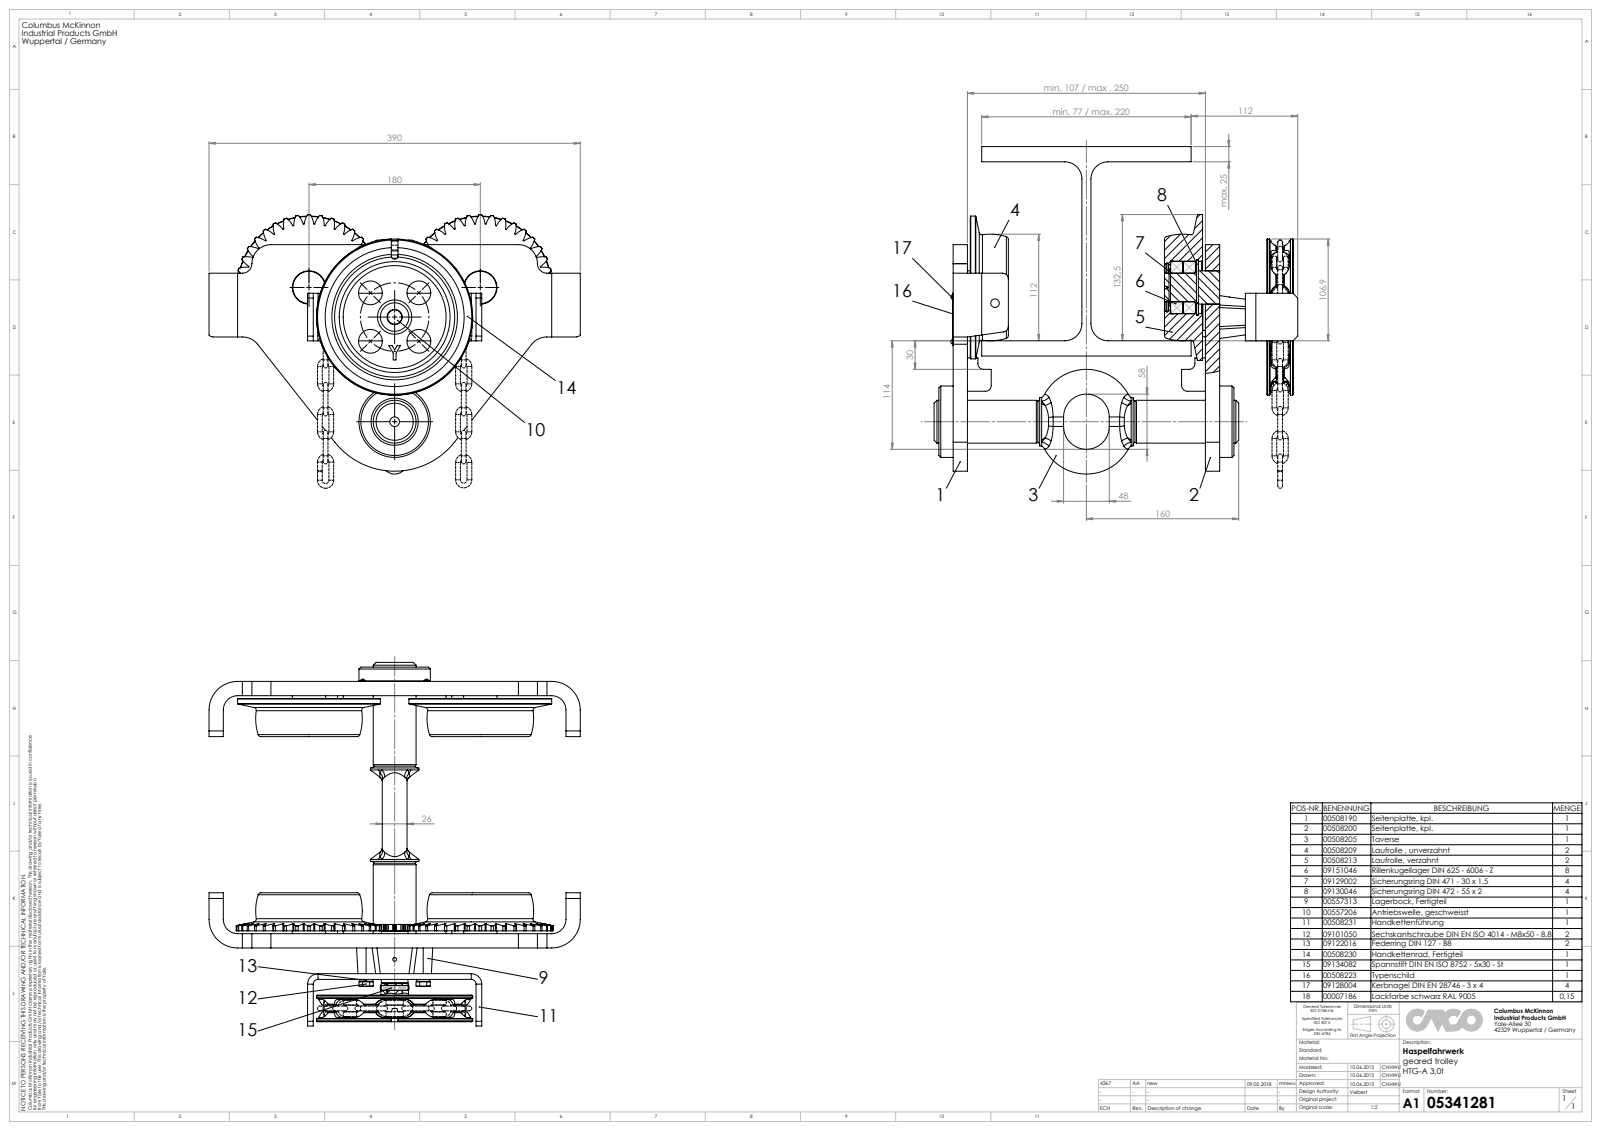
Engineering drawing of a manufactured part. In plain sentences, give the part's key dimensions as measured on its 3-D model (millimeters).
The part is named "HTG-A 3,0t". Its 3-D file was written by "SolidWorks 2015 (AUTOMOTIVE_DESIGN)". It is 72 solids with 2228 faces: 477 planar, 976 cylindrical and 775 other. Overall it measures 500 by 382 by 358.94 millimeters. Its volume is 9 164 000 cubic millimeters and its surface area 1 524 000 square millimeters. Round holes: 10 of diameter 2, 8 of diameter 2.5, 5 of diameter 3, 4 of diameter 3.5, 4 of diameter 9, 4 of diameter 25, 2 of diameter 6.8, 2 of diameter 8.1, 2 of diameter 28.6, 2 of diameter 30, 2 of diameter 35, 2 of diameter 44.4. Round bosses or shafts: 26 of diameter 5, 4 of diameter 5.2, 2 of diameter 150, 2 of diameter 58, 2 of diameter 38.6, 2 of diameter 14.1, 2 of diameter 8, 1 of diameter 164. Partial cylindrical surfaces (rounded edges, fillets, slot ends): 152 of radius 25, 72 of radius 1.5, 24 of radius 10, 22 of radius 1, 8 of radius 2, 8 of radius 2.5, 8 of radius 6, 4 of radius 15. The main face-to-face distances are 204, 16, 15, 220, 135.25, 144.75, 265, 120.25, 129.75, 188. The hole center spacings are 16.8, 25.6, 25.86, 180, 5, 6.25, 8.82, 23.75.
